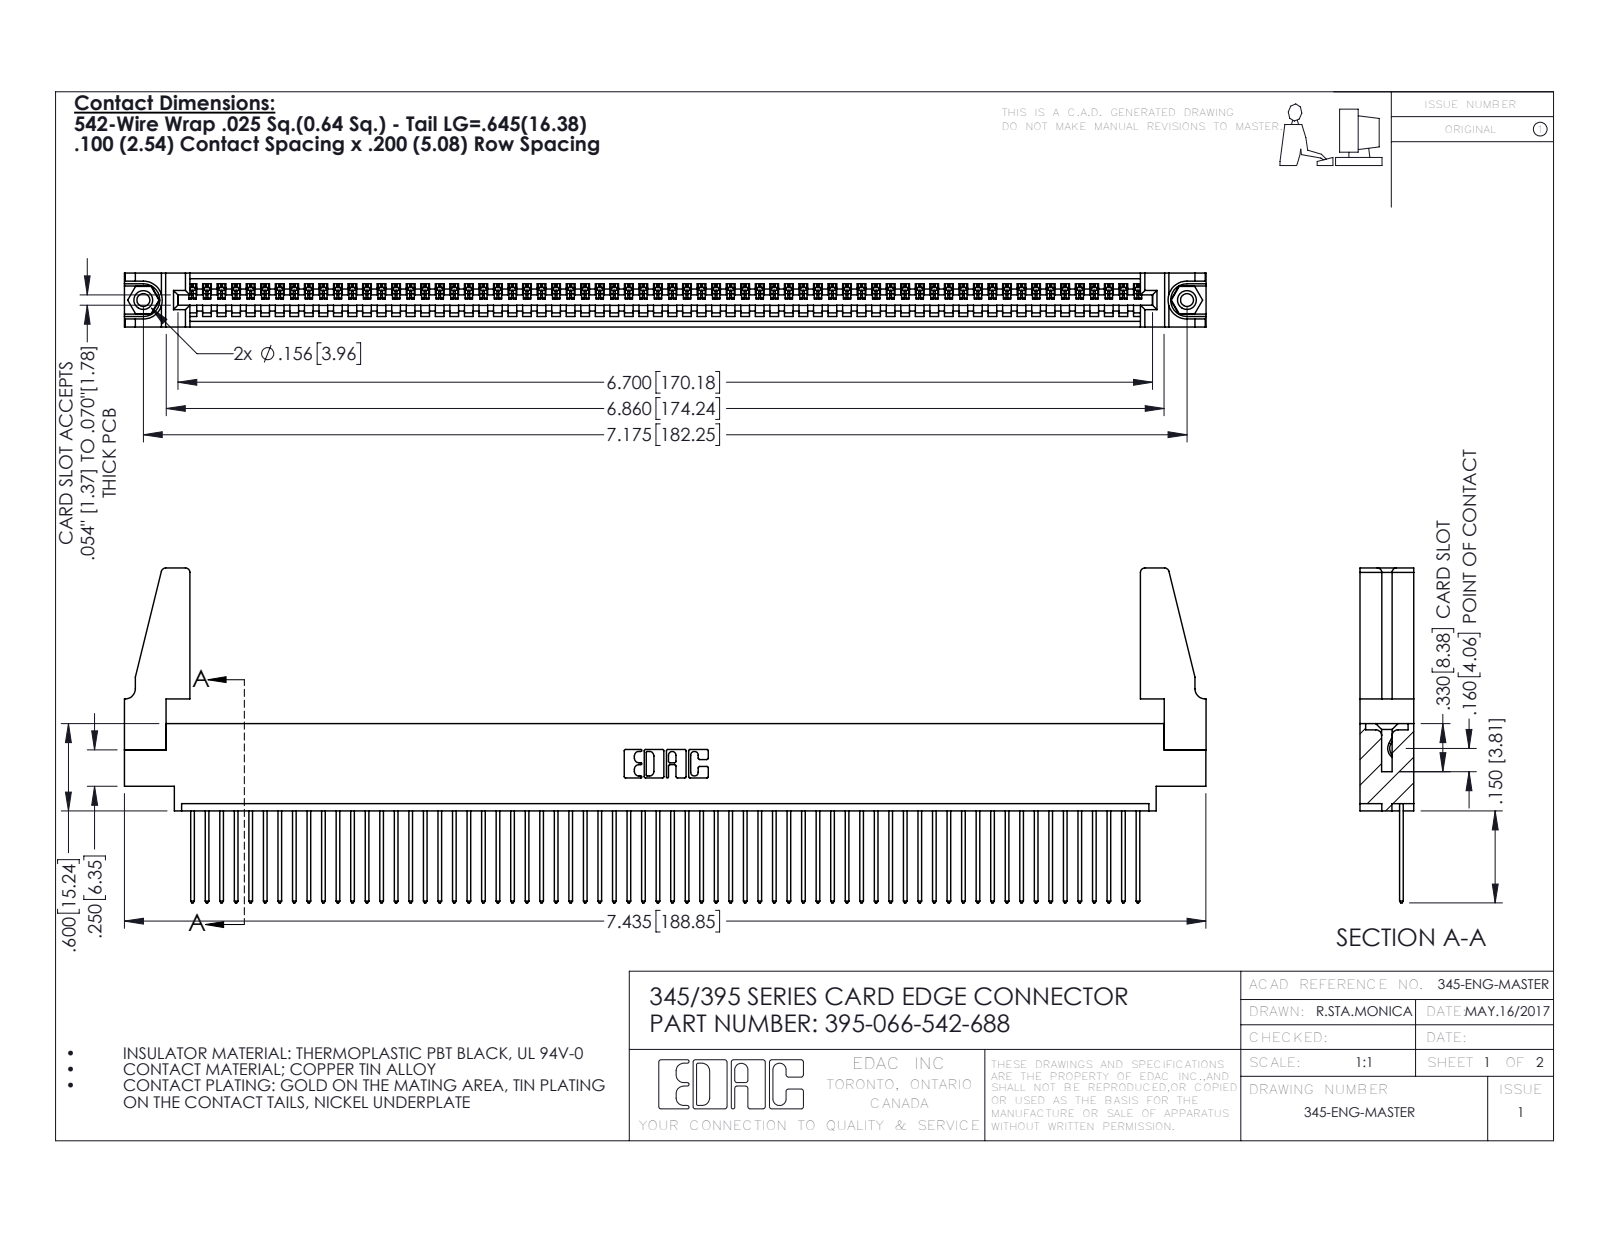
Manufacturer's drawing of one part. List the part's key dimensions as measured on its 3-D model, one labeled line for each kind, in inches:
Part name (STEP PRODUCT): 345-292-001_345-293-142; 395-066-542-688; 345-250-001_345-250-001-102; 345 Part_0.170 Offset - 0.156 Dia-TH (+1 more)
STEP written by: SolidWorks 2016 (CONFIG_CONTROL_DESIGN)
Units: inches
Bodies: 71 solids, 4082 faces (2796 planar, 1270 cylindrical, 16 other)
Overall size (bounding box): 7.436 × 2.302 × 0.37
Volume: 1.307 in³ · Surface area: 44.42 in²
Round holes (diameter × count): ⌀0.089 ×2, ⌀0.125 ×2, ⌀0.156 ×2, ⌀0.064 ×1
Round bosses / shafts (diameter × count): ⌀0.155 ×2
Partial cylindrical surfaces — rounded edges, fillets, slot ends (radius × count): R0.006 ×132, R0.01 ×132, R0.01 ×22, R0.03 ×8, R0.007 ×6, R0.031 ×6, R0.026 ×3, R0.031 ×2
Main face-to-face distances: 0.072, 0.298, 0.37, 0.098, 0.272, 0.025, 0.2, 0.225, 0.175, 0.149
Hole centre spacings: 0.27, 6.939, 7.175
